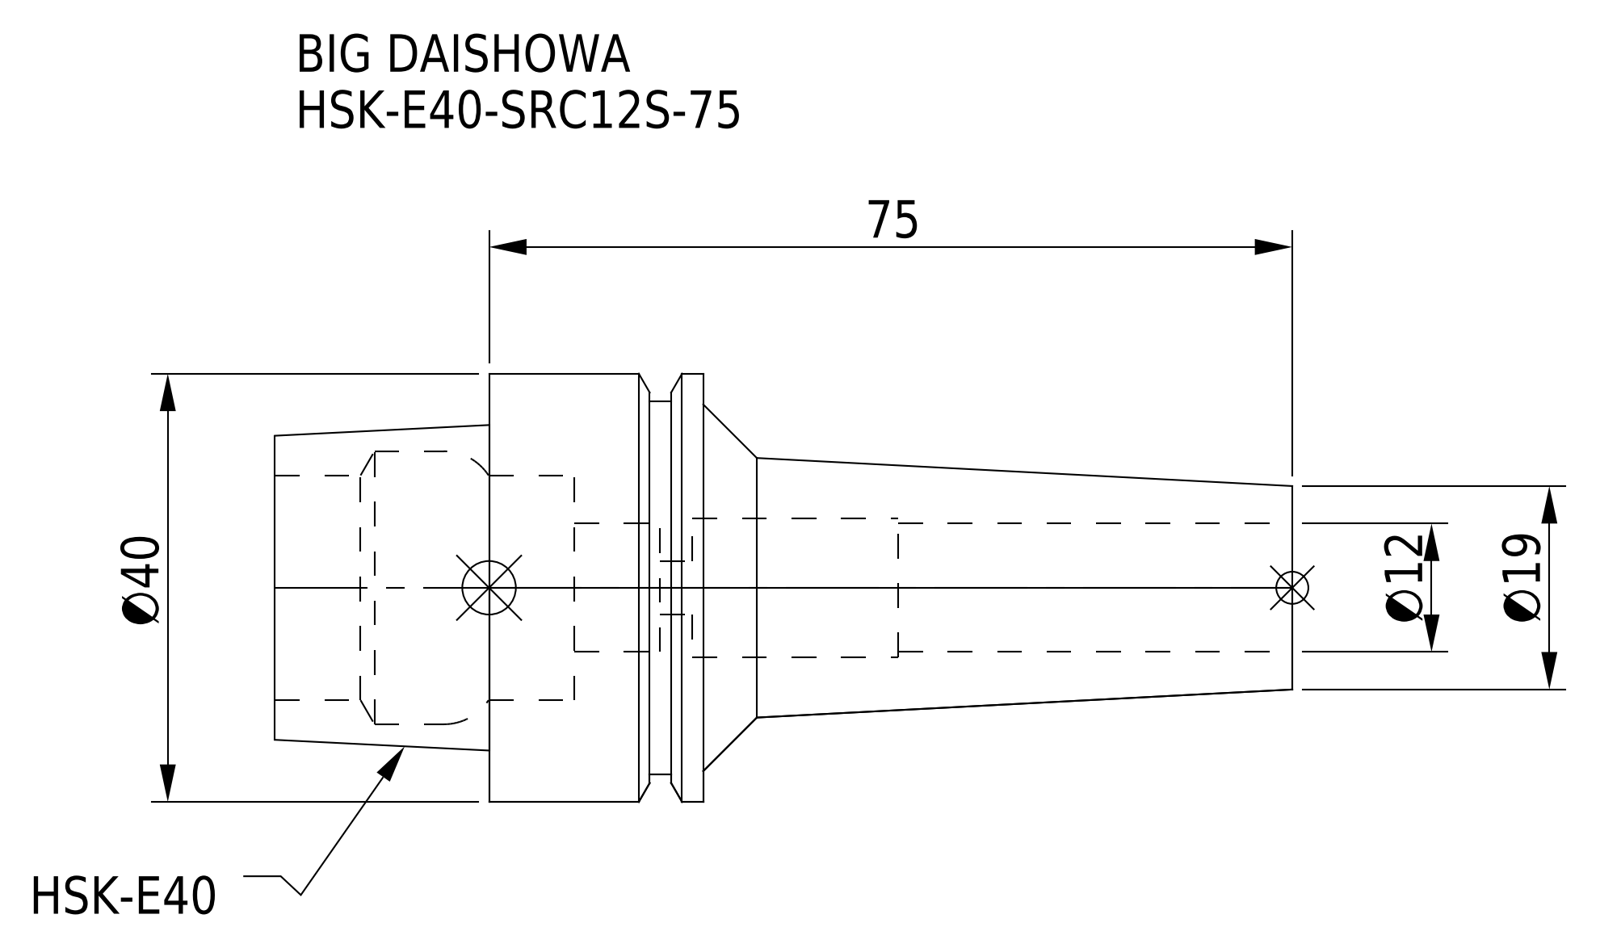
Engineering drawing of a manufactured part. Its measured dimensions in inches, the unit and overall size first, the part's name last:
Units: inches
Overall size (bounding box): 3.74 × 1.575 × 1.575
Round holes (diameter × count): ⌀0.197 ×1, ⌀0.472 ×1, ⌀0.512 ×1, ⌀0.827 ×1, ⌀1.004 ×1
Round bosses / shafts (diameter × count): ⌀1.575 ×1, ⌀1.37 ×1
Main face-to-face distances: 0.787, 1.575, 0.474, 0.313, 1.1, 0.079, 2.165, 2.64, 2.953, 3.74
Volume: 2.485 in³ · Surface area: 23.62 in²
Bodies: 1 solid, 46 faces (10 planar, 22 cylindrical, 14 other)
Part name (STEP PRODUCT): HSK-E40-SRC12S-75
STEP written by: CREO PARAMETRIC BY PTC INC, 2016380 (AUTOMOTIVE_DESIGN)
